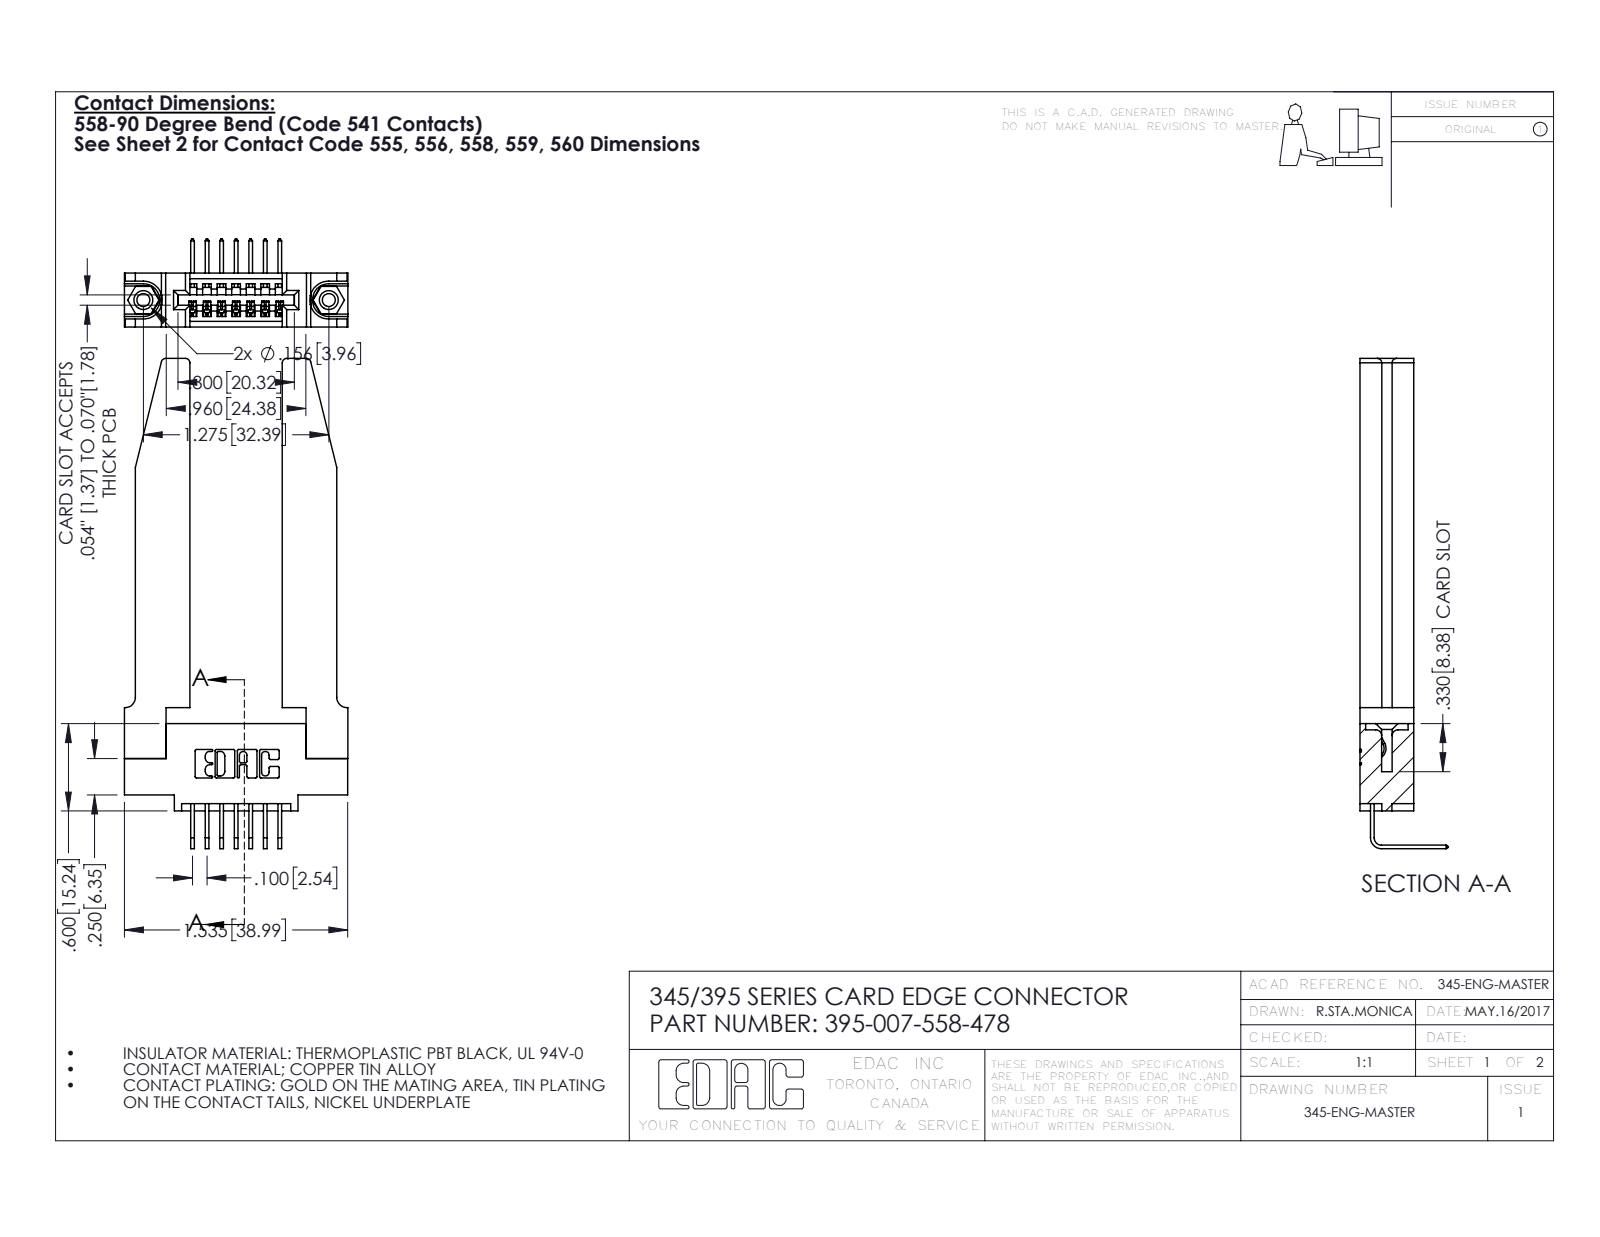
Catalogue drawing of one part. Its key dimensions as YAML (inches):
part_name: "345-220-078_345-220-078; 345-250-001_345-250-001-102; 395-007-558-478; 345 Part_0.110 Offset - 0.156 Dia-TH (+1 more)"
step_written_by: "SolidWorks 2016 (CONFIG_CONTROL_DESIGN)"
units: inches
bodies: {solids: 12, faces: 784, planar: 520, cylindrical: 212, other: 52}
overall_size: [3.369, 1.536, 0.605]
volume: 0.68
surface_area: 17.15
round_holes:
  - {diameter: 0.089, count: 2}
  - {diameter: 0.125, count: 2}
  - {diameter: 0.156, count: 2}
  - {diameter: 0.064, count: 1}
round_bosses_or_shafts:
  - {diameter: 0.155, count: 2}
partial_cylinders:
  - {radius: 0.01, count: 22}
  - {radius: 0.006, count: 14}
  - {radius: 0.03, count: 8}
  - {radius: 0.007, count: 6}
  - {radius: 0.031, count: 6}
  - {radius: 0.026, count: 3}
  - {radius: 0.031, count: 2}
  - {radius: 0.04, count: 2}
face_to_face_distances: [0.37, 0.15, 0.22, 0.072, 0.148, 0.635, 0.298, 0.077, 0.071, 0.055]
hole_center_spacings: [0.27, 1.045, 1.275]
